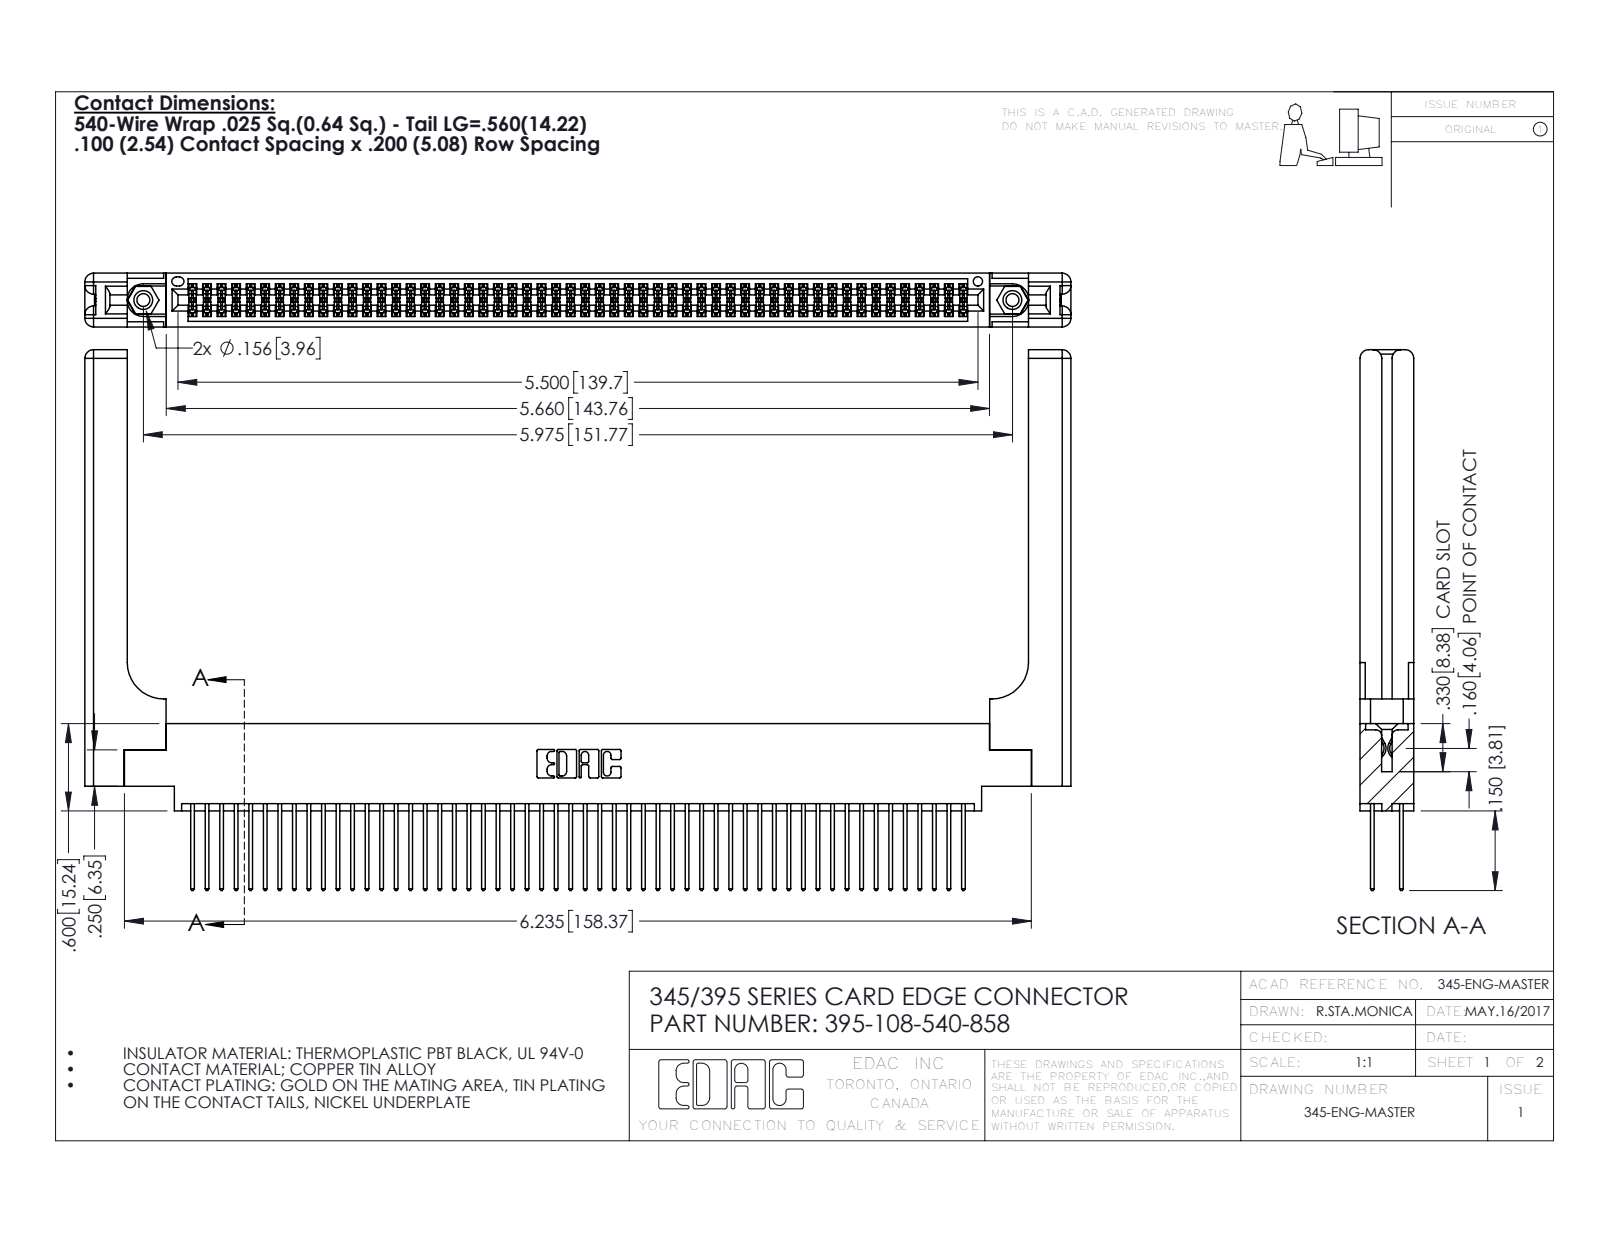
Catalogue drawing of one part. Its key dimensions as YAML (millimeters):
part_name: "345 Part_0.170 Offset - 0.156 Dia-TH; 345-250-001_345-250-001-102; 395-108-540-858; 345-220-058_345-220-058 (+1 more)"
step_written_by: "SolidWorks 2016 (CONFIG_CONTROL_DESIGN)"
units: millimeters
bodies: {solids: 113, faces: 5786, planar: 3796, cylindrical: 1930, other: 60}
overall_size: [172.2, 94.4, 9.4]
volume: 25610
surface_area: 32660
round_holes:
  - {diameter: 2.3, count: 2}
  - {diameter: 3.2, count: 2}
  - {diameter: 4, count: 2}
  - {diameter: 1.6, count: 1}
round_bosses_or_shafts:
  - {diameter: 3.9, count: 2}
partial_cylinders:
  - {radius: 0.2, count: 162}
  - {radius: 0.3, count: 108}
  - {radius: 0.3, count: 22}
  - {radius: 1.5, count: 16}
  - {radius: 0.2, count: 6}
  - {radius: 0.8, count: 6}
  - {radius: 0.7, count: 3}
  - {radius: 0.4, count: 2}
face_to_face_distances: [1.8, 7.6, 9.4, 2.5, 6.9, 0.6, 5.1, 5.7, 4.4, 3.8]
hole_center_spacings: [6.9, 145.8, 151.8]
